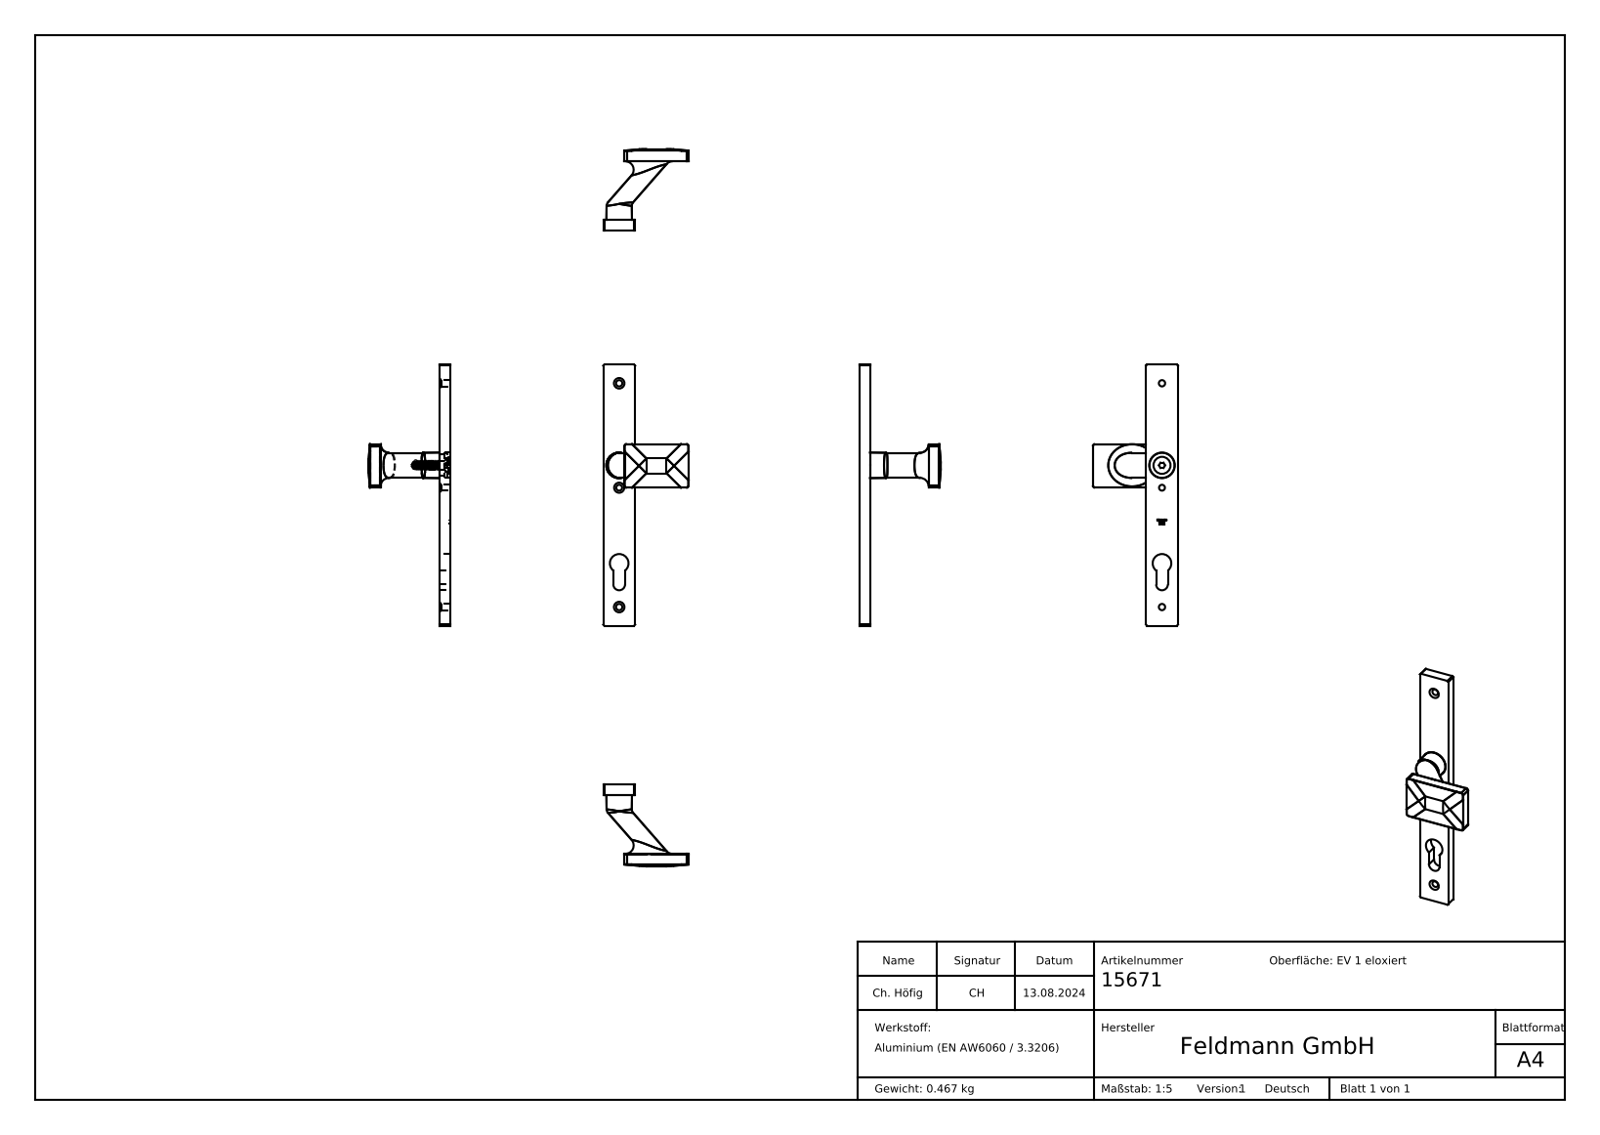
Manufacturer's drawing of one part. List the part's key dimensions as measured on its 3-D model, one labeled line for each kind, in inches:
Part name (STEP PRODUCT): 15671 Teil 3_15671 Teil1a Keyshot; 15671 Teil 3_15671 Teil1 Keyshot; DIN 7991 Konfig_M8x20 Keyshot; 15671 Teil 2_15671 Teil2 Keyshot (+1 more)
STEP written by: SolidWorks 2018 (CONFIG_CONTROL_DESIGN)
Units: inches
Bodies: 4 solids, 187 faces (34 planar, 75 cylindrical, 78 other)
Overall size (bounding box): 9.646 × 3.011 × 2.953
Volume: 7.187 in³ · Surface area: 53.42 in²
Round holes (diameter × count): ⌀0.232 ×2, ⌀0.217 ×1, ⌀0.268 ×1, ⌀0.512 ×1, ⌀0.787 ×1, ⌀0.945 ×1
Round bosses / shafts (diameter × count): ⌀0.925 ×1, ⌀0.63 ×1, ⌀0.315 ×1
Partial cylindrical surfaces — rounded edges, fillets, slot ends (radius × count): R0.004 ×28, R0.012 ×8, R3.15 ×5, R0.079 ×4, R0.217 ×1, R0.344 ×1
Main face-to-face distances: 0.394, 1.181, 2.559, 2.165, 0.197, 2.362, 0.591, 1.614, 2.953, 1.772
Hole centre spacings: 0.827, 3.031, 3.858, 4.409, 5.236, 8.268
